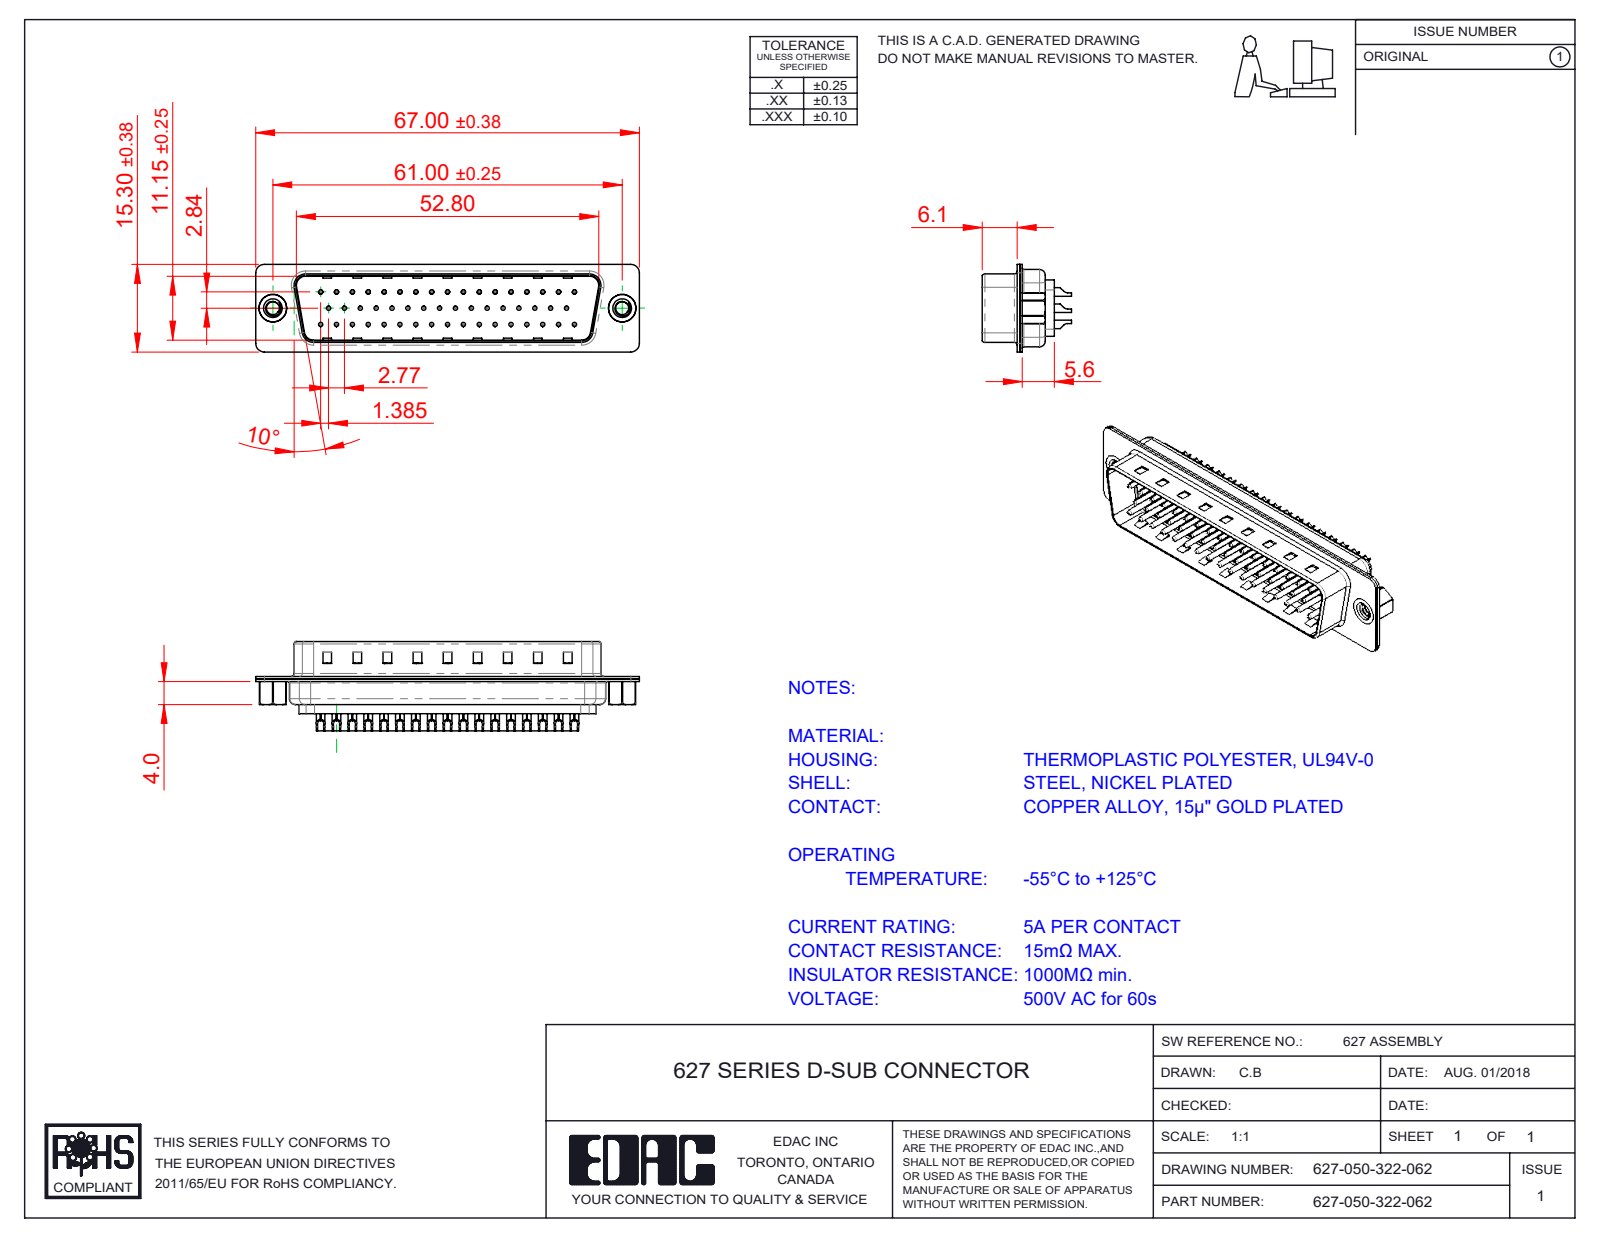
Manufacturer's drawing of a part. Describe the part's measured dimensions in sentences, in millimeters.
The part is named "627-050-322-062; 627 Housing_50 LP; 627 4-40 Threaded Rivet; 627 Contact Row 1_22L (+4 more)". Its 3-D file was written by "SolidWorks 2020 (CONFIG_CONTROL_DESIGN)". It is 55 solids with 3608 faces: 903 planar, 1589 cylindrical and 1116 other. Overall it measures 67 by 15.6 by 15.3 millimeters. Its volume is 4 447 cubic millimeters and its surface area 12 763 square millimeters. Round holes: 58 of diameter 1.6, 50 of diameter 0.35, 50 of diameter 1.1, 8 of diameter 0.75, 8 of diameter 2, 2 of diameter 2.26, 2 of diameter 4, 2 of diameter 4.8. Round bosses or shafts: 50 of diameter 2, 50 of diameter 1.5, 50 of diameter 0.75, 2 of diameter 5, 2 of diameter 4.9. Partial cylindrical surfaces (rounded edges, fillets, slot ends): 16 of radius 1.5, 12 of radius 2, 8 of radius 0.5, 8 of radius 1.6, 7 of radius 1, 4 of radius 0.25, 4 of radius 0.6, 4 of radius 0.65. The main face-to-face distances are 0.4, 0.45, 11.55, 0.9, 6.05, 6.5, 0.78, 1.95, 0.77, 12.33. The hole center spacings are 2.77, 3.16, 5.54, 8.31, 11.08, 13.85, 16.62, 19.39.
